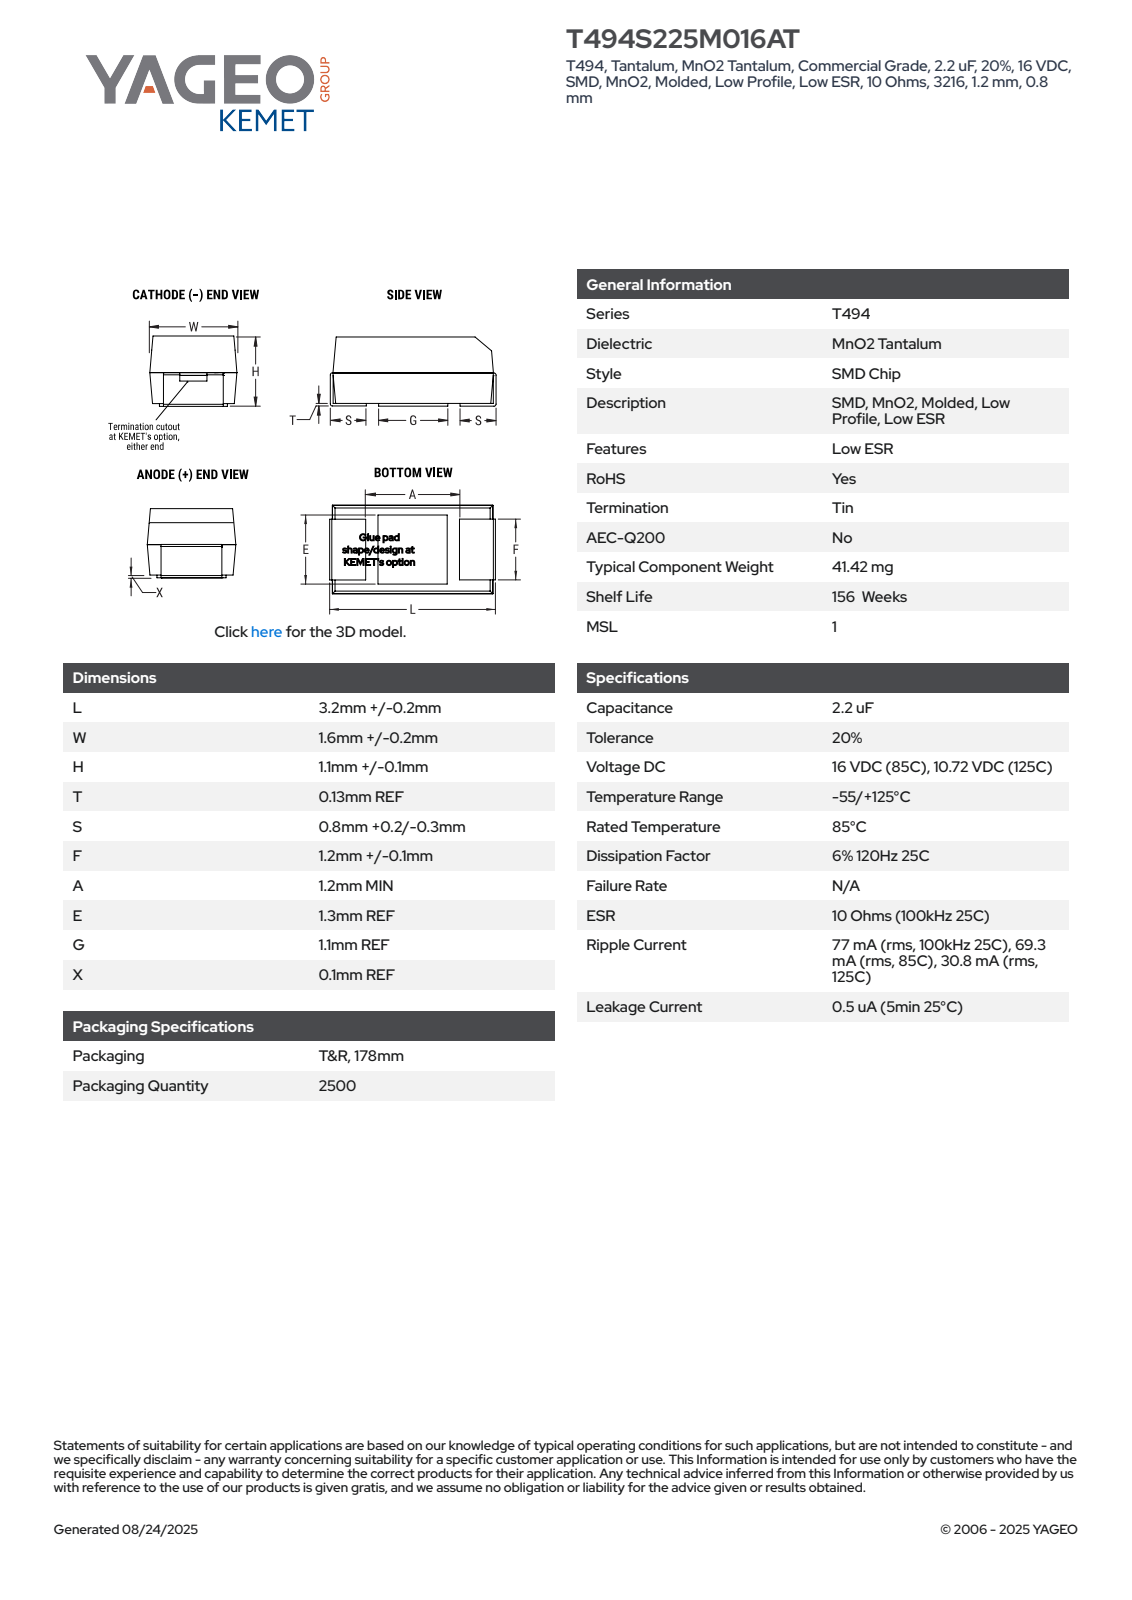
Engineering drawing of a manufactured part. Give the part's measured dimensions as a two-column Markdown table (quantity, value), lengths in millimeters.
| quantity | value |
| --- | --- |
| part name | CTSM_TCM2NBKRP_3216_L3.4W1.8H1.2T0.13S0.8F1.3A1.2E1.3G1.1X0.1 |
| STEP written by | SolidWorks 2020 (AUTOMOTIVE_DESIGN) |
| units | millimeters |
| bodies | 4 solids, 94 faces (90 planar, 4 cylindrical, 0 other) |
| overall size | 3.4 × 1.8 × 1.21 |
| volume | 6 mm³ |
| surface area | 24 mm² |
| partial cylindrical surfaces (radius × count) | 0.1 × 4 |
| main face-to-face distances | 1.2, 1.1, 1.77, 1.78, 3.27, 3.4, 3.14, 1.15, 2.25, 1.02 |
